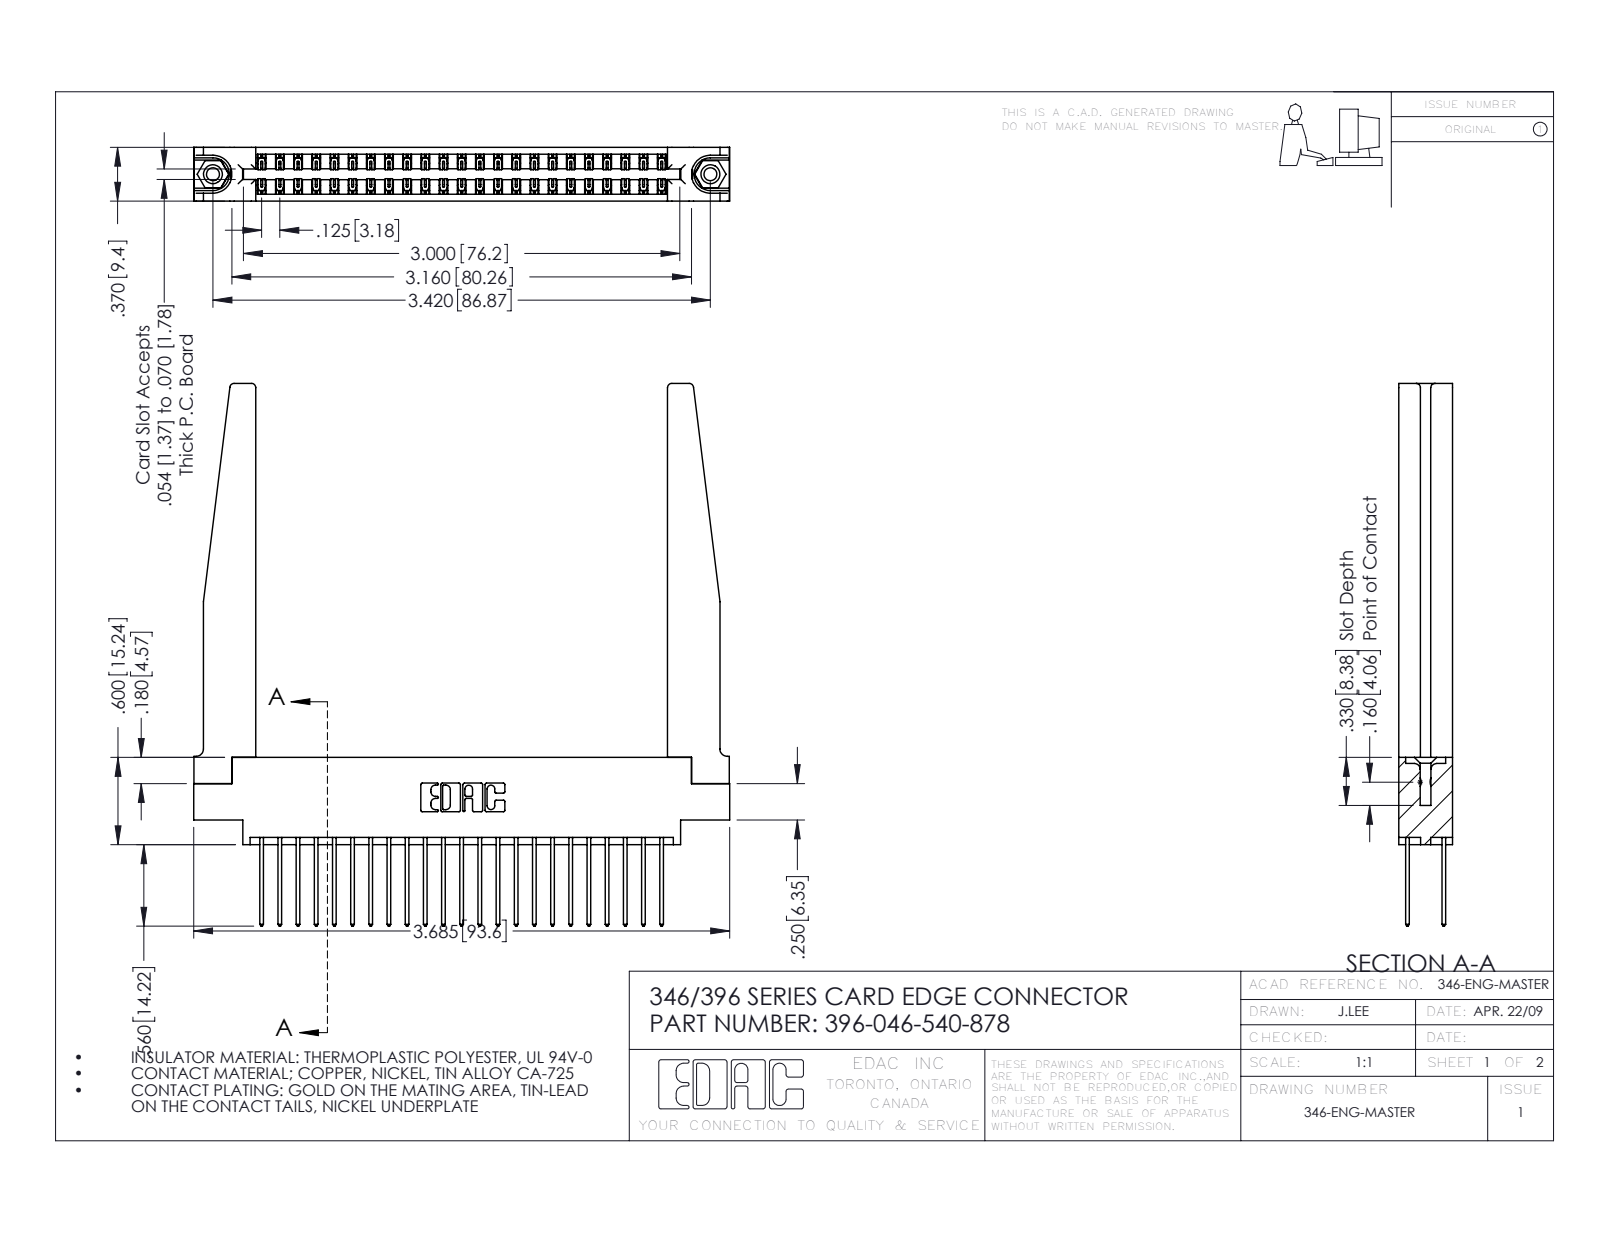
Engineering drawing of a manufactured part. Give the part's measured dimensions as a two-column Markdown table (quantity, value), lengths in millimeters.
| quantity | value |
| --- | --- |
| part name | 346 Part_0.170 Offset - 0.156 Dia-TH; 396-046-540-878; 345-250-001_345-250-001-102; 346-220-078_345-220-078 (+1 more) |
| STEP written by | SolidWorks 2016 (CONFIG_CONTROL_DESIGN) |
| units | millimeters |
| bodies | 51 solids, 2752 faces (1832 planar, 868 cylindrical, 52 other) |
| overall size | 94.7 × 93.6 × 9.4 |
| volume | 15 900 mm³ |
| surface area | 19 610 mm² |
| round holes (diameter × count) | 2.3 × 2, 3.2 × 2, 4 × 2, 1.6 × 1 |
| round bosses / shafts (diameter × count) | 3.9 × 2 |
| partial cylindrical surfaces (radius × count) | 0.2 × 69, 0.3 × 46, 0.3 × 22, 0.8 × 8, 0.2 × 6, 0.8 × 6, 0.7 × 3, 0.4 × 2 |
| main face-to-face distances | 9.4, 1.2, 8.2, 1.8, 6.4, 3.8, 3.8, 7.6, 0.6, 7 |
| hole center spacings | 6.2, 81.6, 86.9 |
